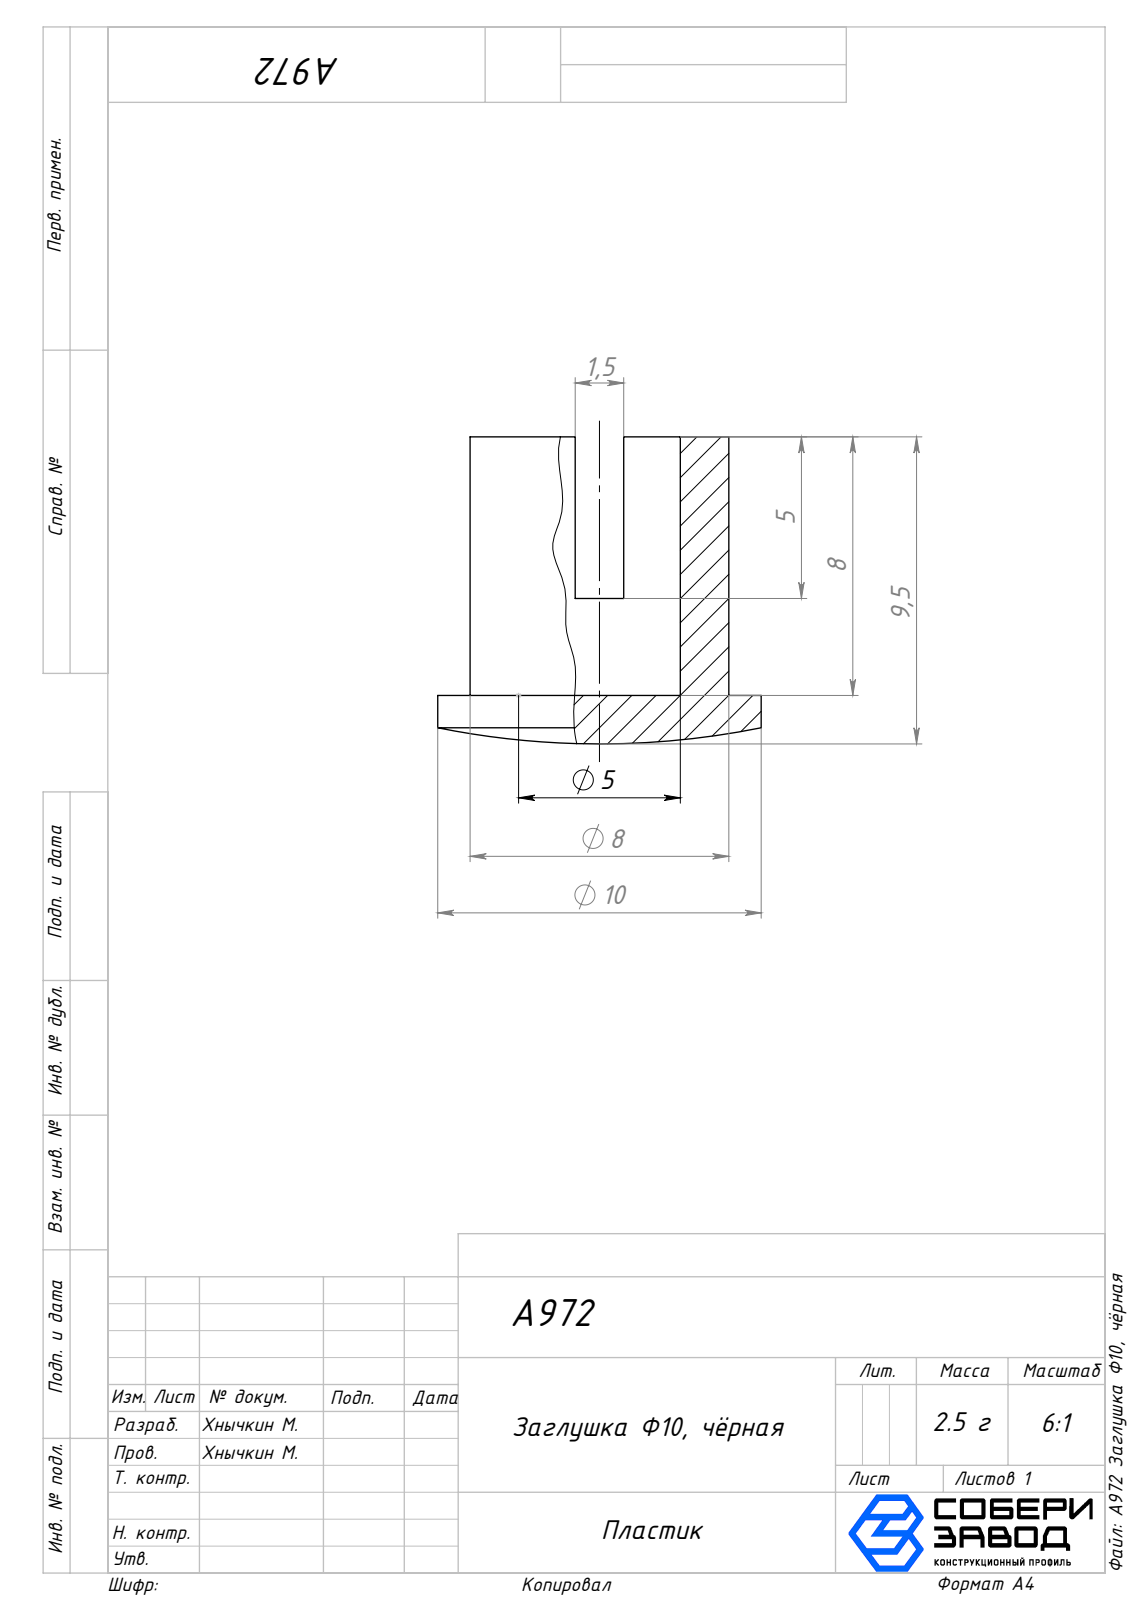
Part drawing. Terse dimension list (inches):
name: A972 Заглушка Ф10, чёрная
written by: SolidWorks 2025 (AUTOMOTIVE_DESIGN)
unit: in
bodies: 1 solid, 18 faces (10 planar, 6 cylindrical, 2 other)
size: 0.394 × 0.394 × 0.374
volume: 0.02 in³; area: 0.801 in²
holes: 1× ⌀0.197
bosses: 1× ⌀0.394, 1× ⌀0.315
face distances: 0.315, 0.059, 0.118, 0.197
